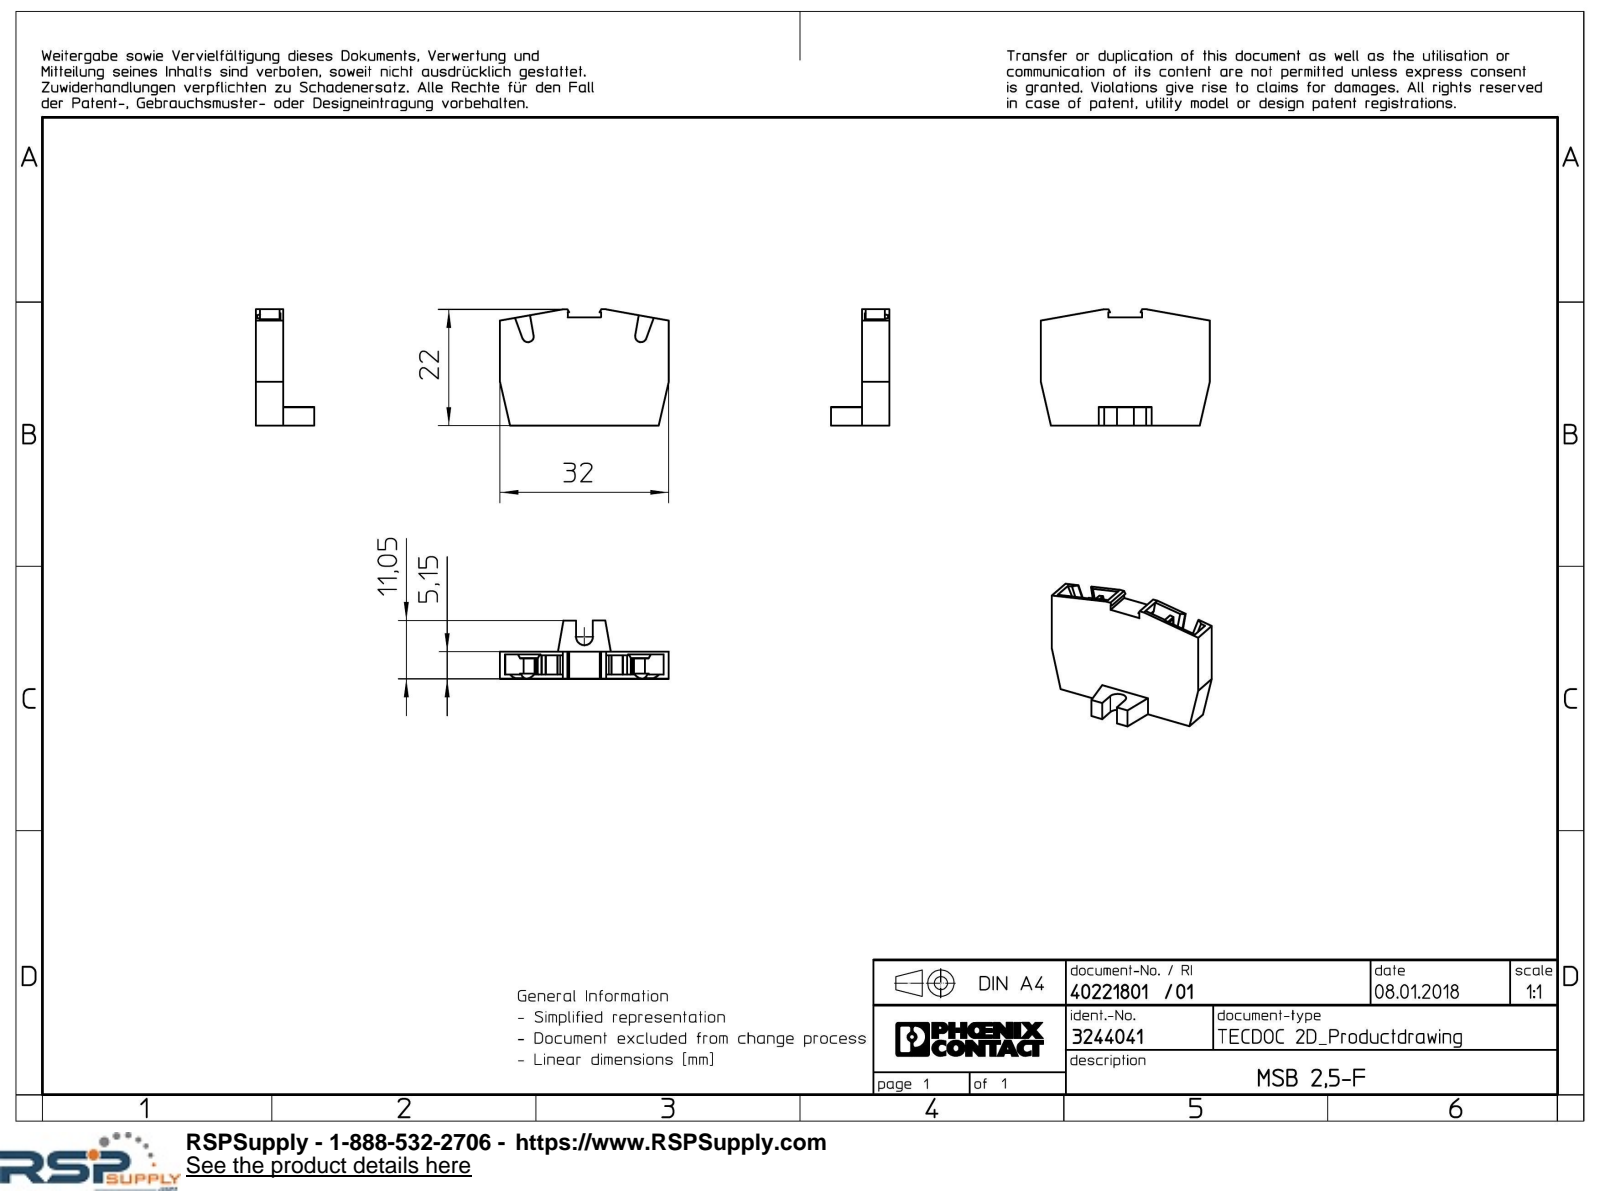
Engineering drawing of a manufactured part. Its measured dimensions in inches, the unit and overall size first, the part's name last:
Units: inches
Overall size (bounding box): 1.26 × 0.866 × 0.435
Partial cylindrical surfaces — rounded edges, fillets, slot ends (radius × count): R0.039 ×4, R0.047 ×4, R0.094 ×2, R0.103 ×2, R0.063 ×1
Main face-to-face distances: 0.203, 0.144, 0.171, 0.031, 0.028, 0.175, 0.02, 0.152, 0.183, 1.26
Volume: 0.168 in³ · Surface area: 4.17 in²
Bodies: 1 solid, 100 faces (87 planar, 13 cylindrical, 0 other)
Part name (STEP PRODUCT): MSB_2.5_F-select
STEP written by: Creo Elements/Direct Modeling 20.1A 29-Sep-2018 (C) Parametric Technology GmbH (AUTOMOTIVE_DESIGN)
